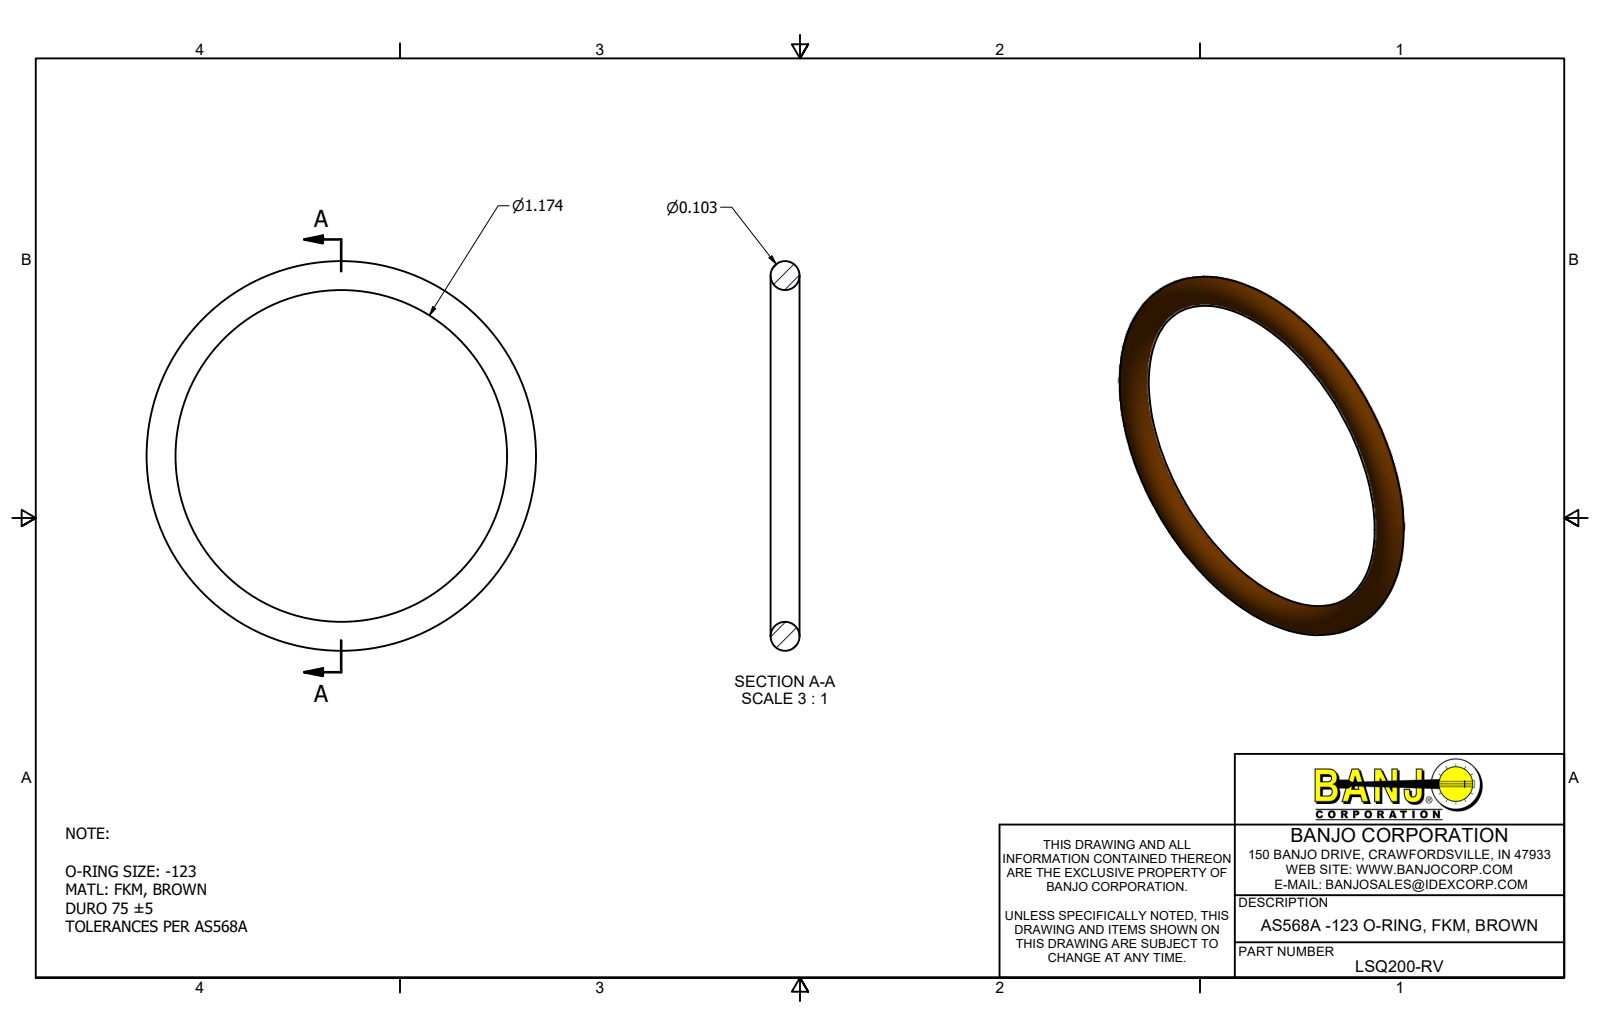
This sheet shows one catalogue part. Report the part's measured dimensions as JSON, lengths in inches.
{"part_name": "LSQ200-RV", "step_written_by": "Autodesk Inventor 2019 (AUTOMOTIVE_DESIGN)", "units": "inches", "bodies": {"solids": 1, "faces": 1, "planar": 0, "cylindrical": 0, "other": 1}, "overall_size": [1.38, 1.38, 0.103], "volume_in3": 0.033, "surface_area_in2": 1.298}
